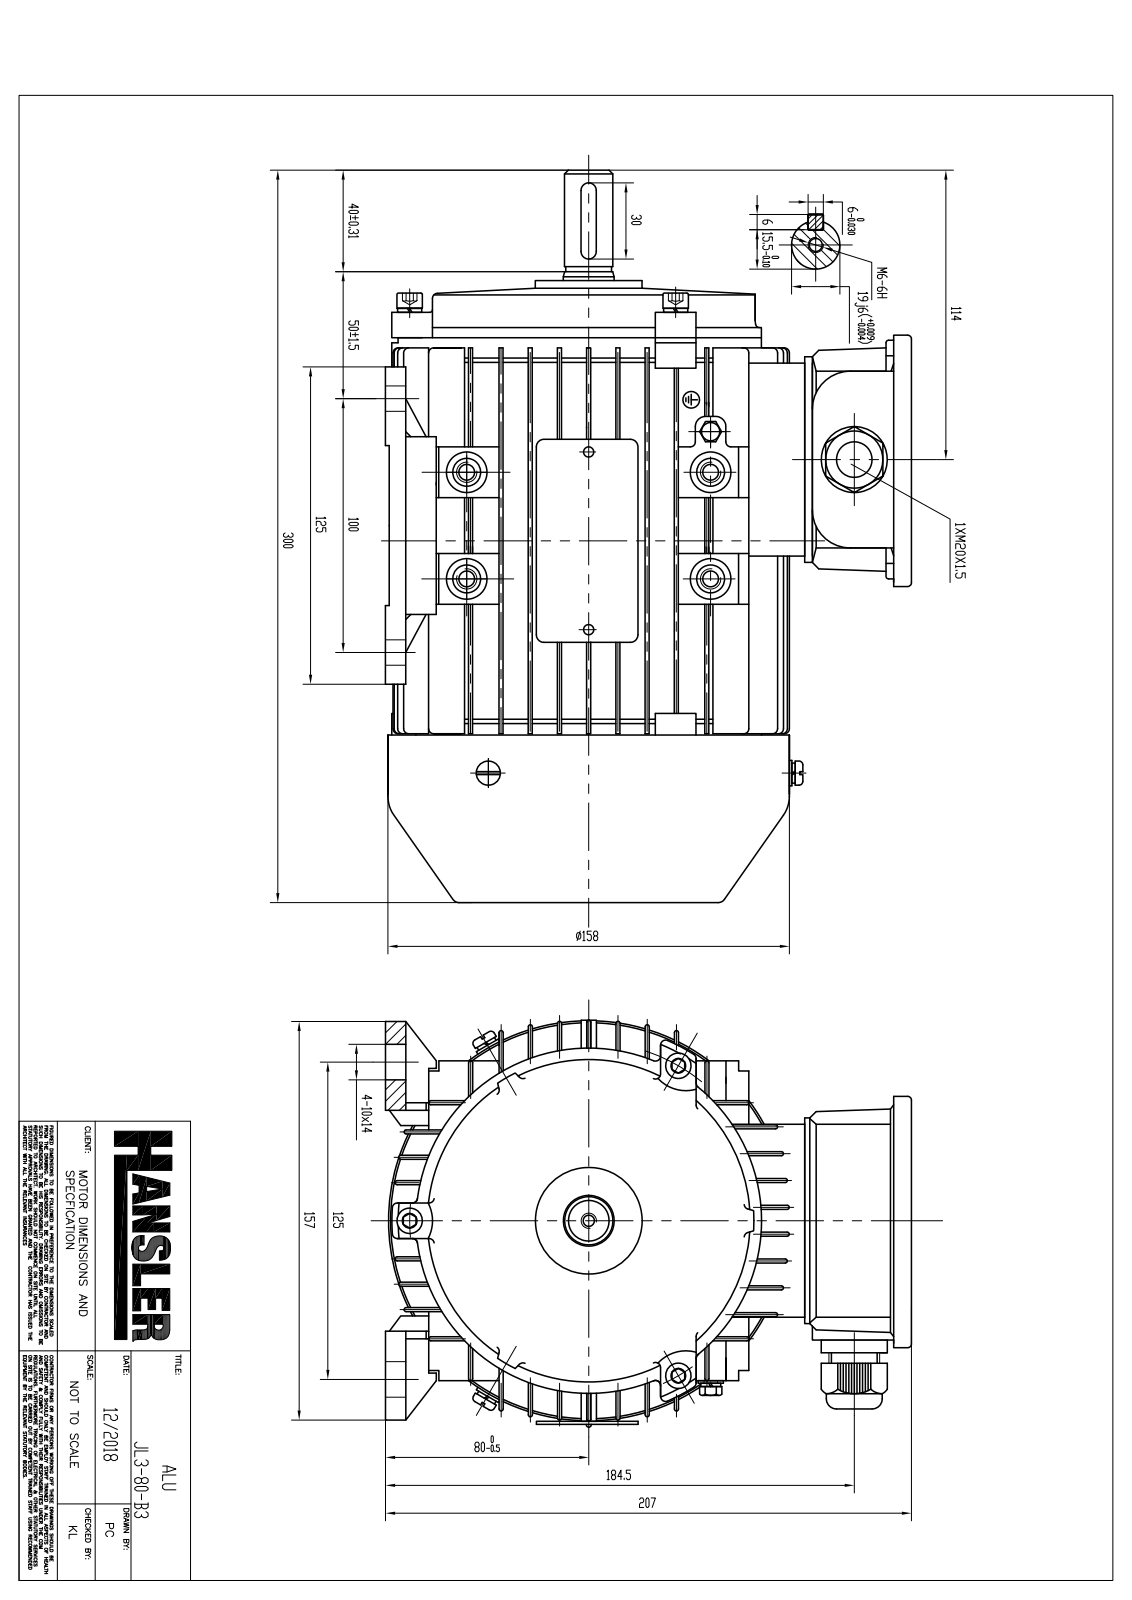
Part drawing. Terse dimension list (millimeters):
name: JL3-80-B3
written by: DATAKIT 2018 (c) (AP242_MANAGED_MODEL_BASED_3D_ENGINEERING_MIM_LF)
unit: mm
bodies: 48 solids, 2493 faces (1276 planar, 720 cylindrical, 497 other)
size: 304.48 × 210.72 × 158
volume: 1 132 000 mm³; area: 663 972 mm²
holes: 13× ⌀4, 10× ⌀16, 8× ⌀6.6, 4× ⌀5.25, 4× ⌀5.3, 4× ⌀5.8, 4× ⌀9, 4× ⌀12, 3× ⌀6.39, 3× ⌀7, 2× ⌀2, 2× ⌀9.6
bosses: 8× ⌀11, 5× ⌀18, 4× ⌀15, 4× ⌀13, 4× ⌀12, 4× ⌀10, 4× ⌀8, 4× ⌀7.85
rounds: 72× R1, 70× R2, 31× R3, 20× R0.33, 20× R5, 16× R0.3, 12× R0.39, 12× R1.97
face distances: 1.6, 11.5, 23, 34.5, 10.57, 46, 9.9, 13.1, 21.14, 21.4
hole spacings: 31.91, 45.8, 14.14, 42, 54, 87, 96, 104.79
